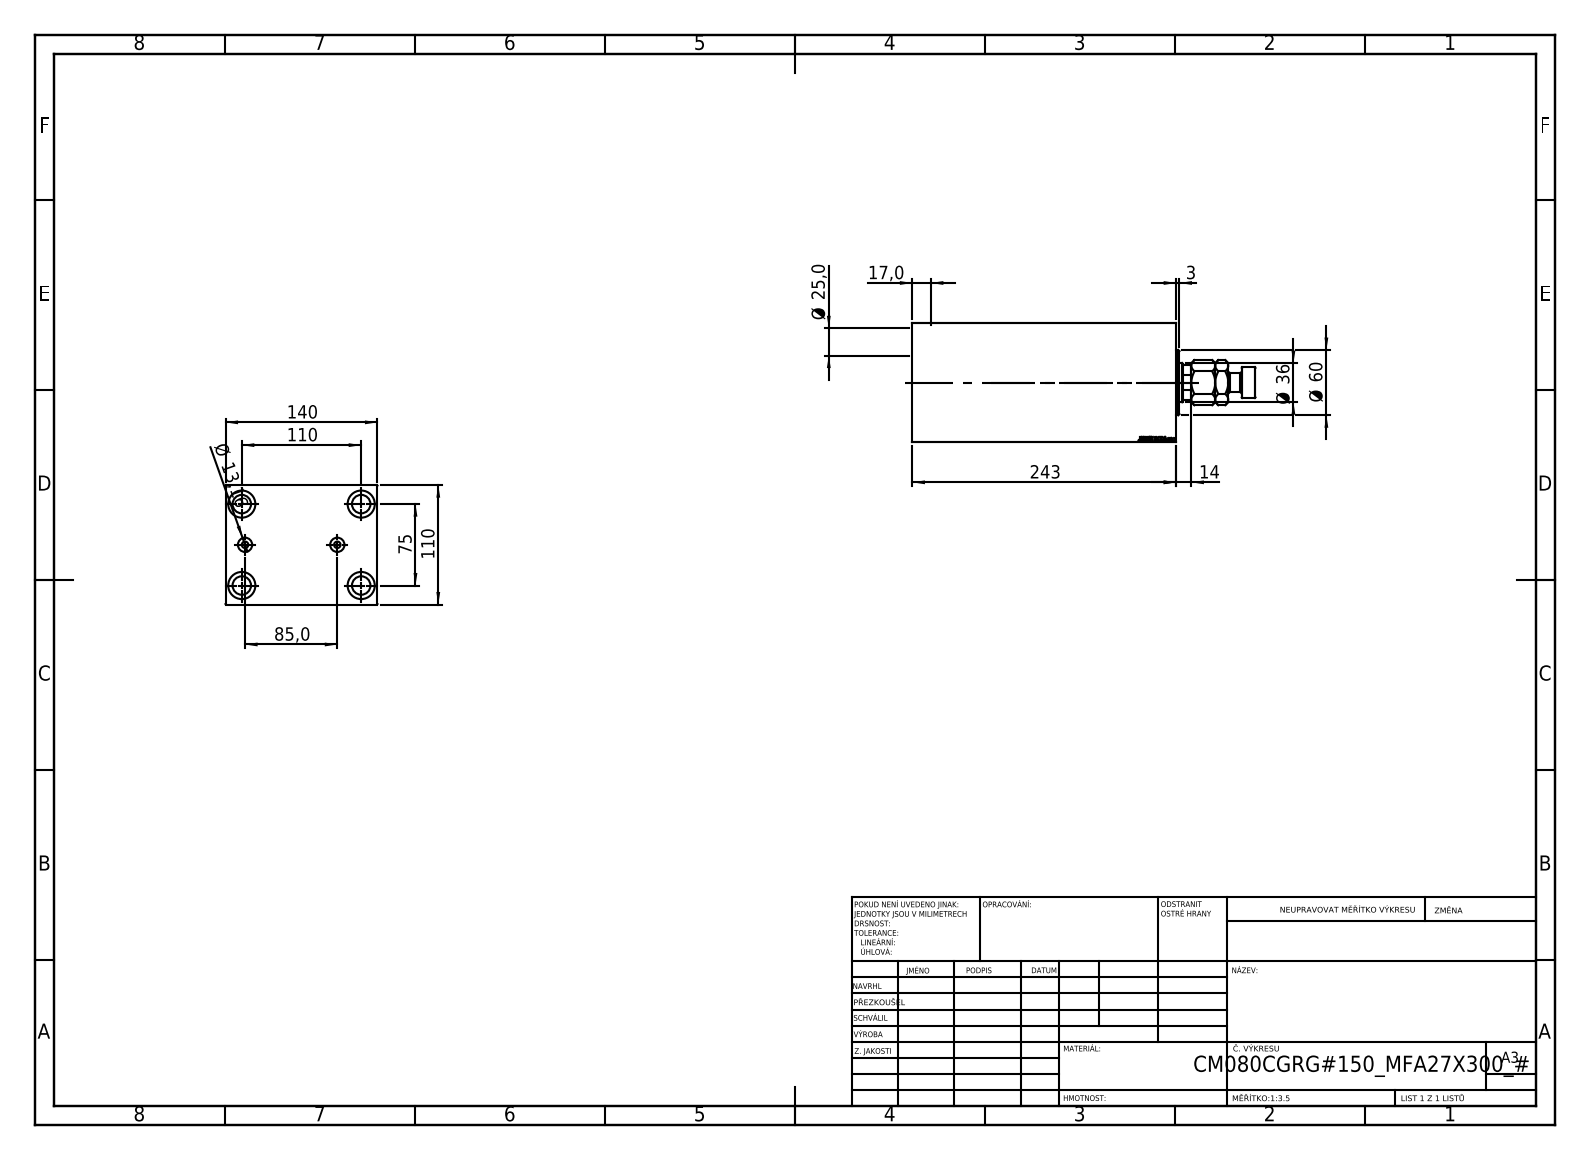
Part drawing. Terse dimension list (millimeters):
name: MFA; V450CM_C_Body; V450CM_VC_B; V450CM_C_VCP
written by: SolidWorks 2019 (CONFIG_CONTROL_DESIGN)
unit: mm
bodies: 4 solids, 912 faces (424 planar, 62 cylindrical, 426 other)
size: 316 × 140 × 110
volume: 2 924 000 mm³; area: 338 799 mm²
holes: 4× ⌀17, 4× ⌀25, 2× ⌀6, 2× ⌀13.16, 1× ⌀25.5, 1× ⌀36, 1× ⌀39.5, 1× ⌀80, 1× ⌀82, 1× ⌀87
bosses: 1× ⌀60, 1× ⌀28, 1× ⌀18
rounds: 1× R17.5
face distances: 110, 140, 243, 222, 21, 14, 229, 208, 164, 150
hole spacings: 66.57, 37.62, 43.48, 75, 95.66, 110, 113.38, 133.14
